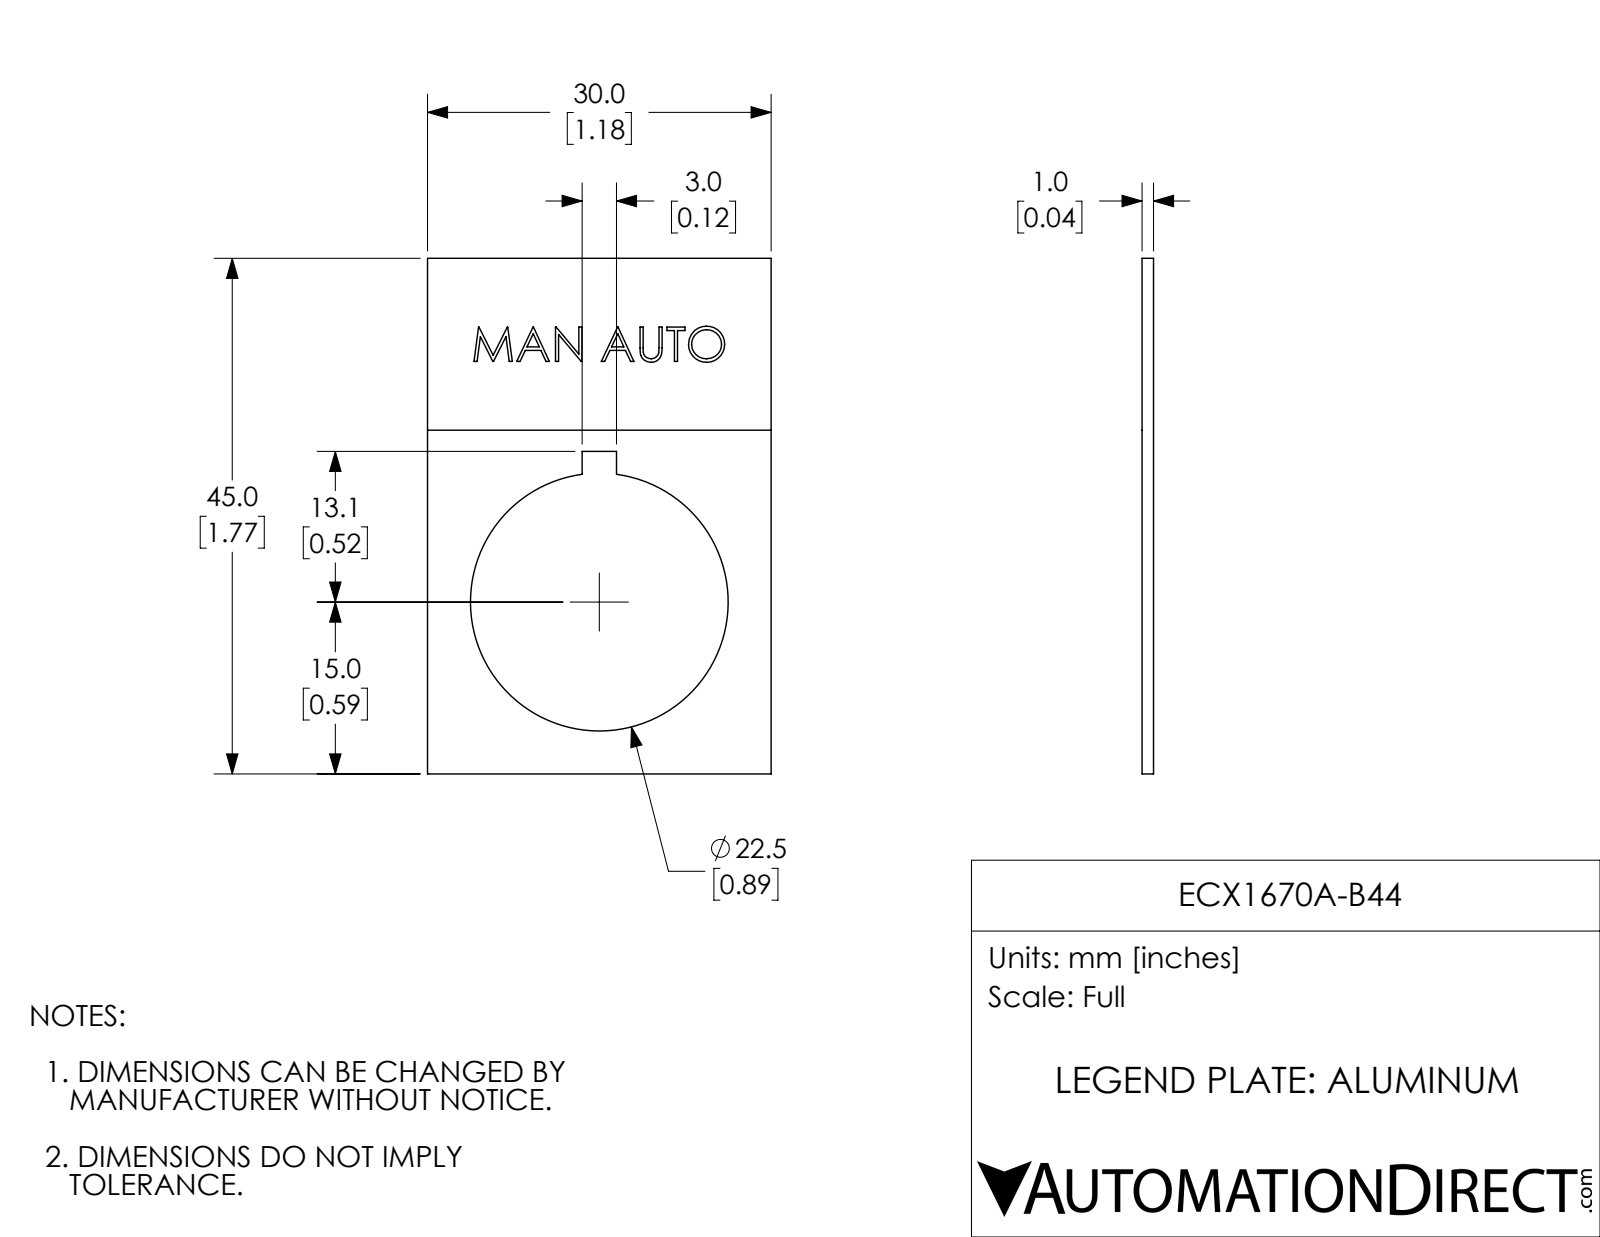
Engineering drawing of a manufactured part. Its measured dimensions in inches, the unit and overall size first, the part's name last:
Units: inches
Overall size (bounding box): 1.772 × 1.181 × 0.039
Round holes (diameter × count): ⌀0.886 ×1
Main face-to-face distances: 0.039, 1.181, 1.772, 0.038, 0.531, 0.65, 1.108, 0.663, 0.118, 0.21
Volume: 0.058 in³ · Surface area: 3.287 in²
Bodies: 1 solid, 97 faces (79 planar, 3 cylindrical, 15 other)
Part name (STEP PRODUCT): ECX1670A-B44
STEP written by: SolidWorks 2017 (AUTOMOTIVE_DESIGN)
